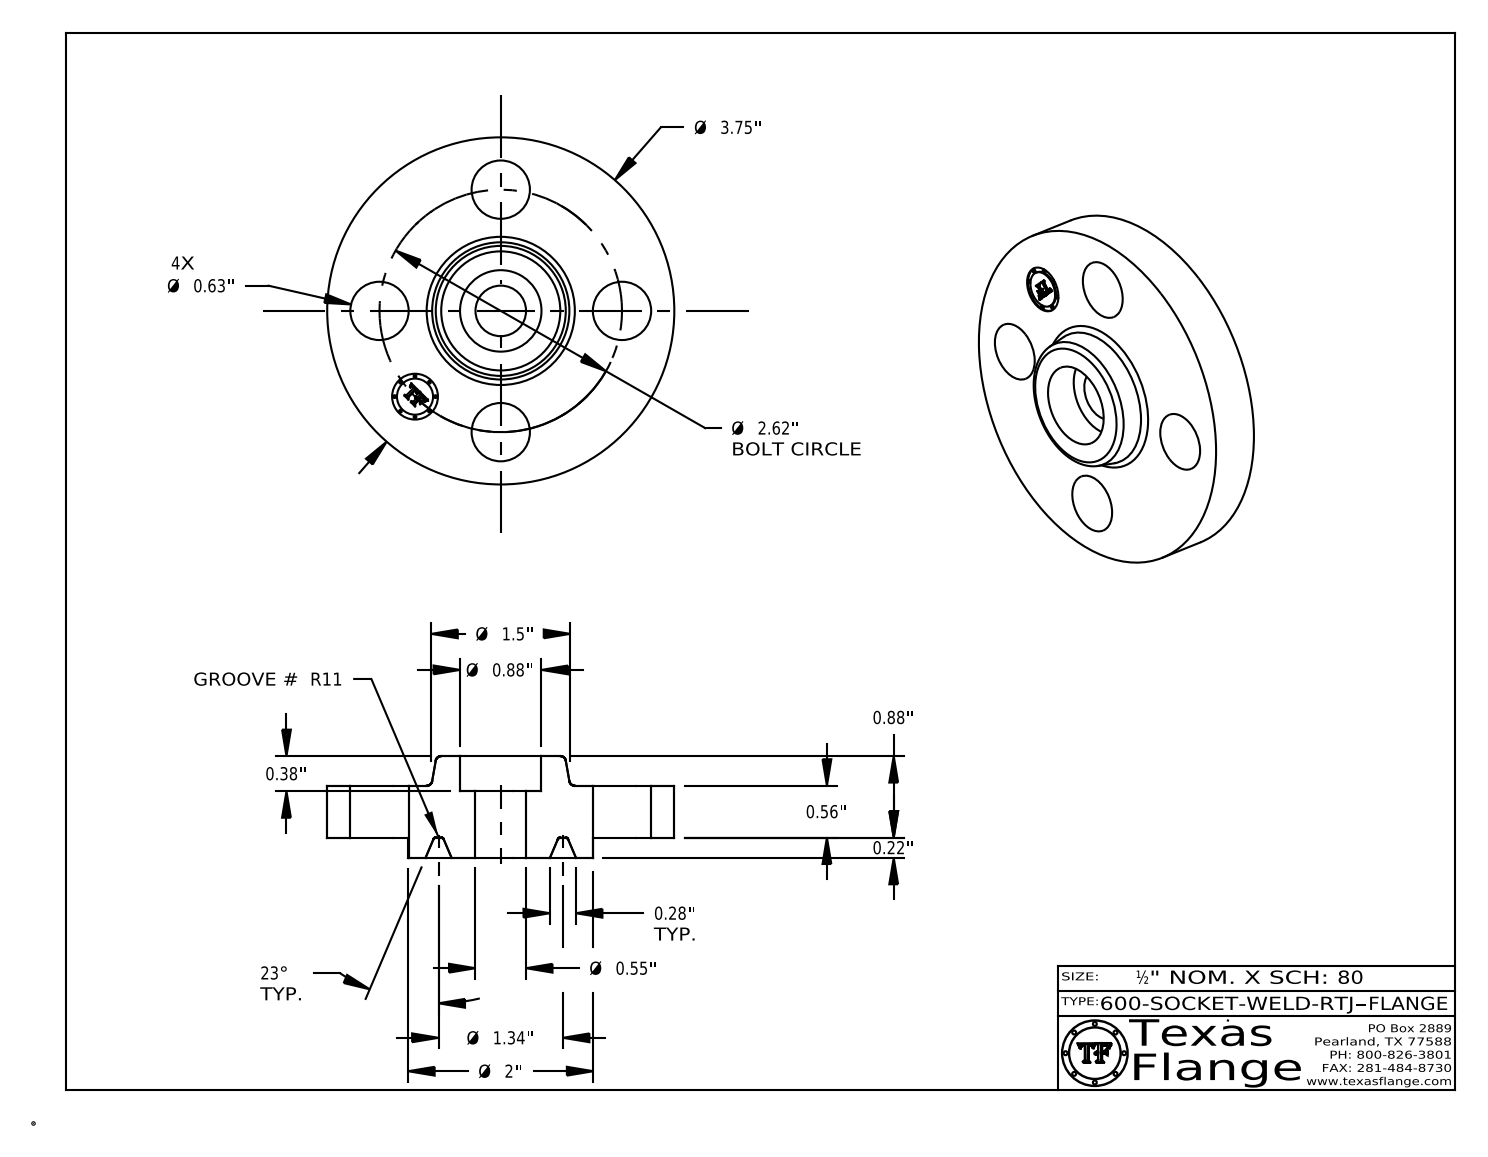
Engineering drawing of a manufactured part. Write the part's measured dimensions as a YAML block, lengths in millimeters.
part_name: "600-SOCKET-WELD-RTJ"
step_written_by: "CATIA V5 STEP AP214 (AUTOMOTIVE_DESIGN)"
units: millimeters
bodies: {solids: 1, faces: 426, planar: 372, cylindrical: 40, other: 14}
overall_size: [95.3, 95.3, 27.9]
volume: 100400
surface_area: 23330
round_holes:
  - {diameter: 16, count: 4}
  - {diameter: 12.6, count: 1}
  - {diameter: 13.9, count: 1}
  - {diameter: 22.4, count: 1}
round_bosses_or_shafts:
  - {diameter: 0.8, count: 8}
  - {diameter: 95.3, count: 1}
  - {diameter: 50.8, count: 1}
  - {diameter: 9.9, count: 1}
face_to_face_distances: [14.2, 5.6, 19.8, 27.9, 22.4, 8.1, 18.3, 12.7, 1.5, 9.7]
hole_center_spacings: [33.3, 47, 25.5, 61.5, 66.5, 33.3]
